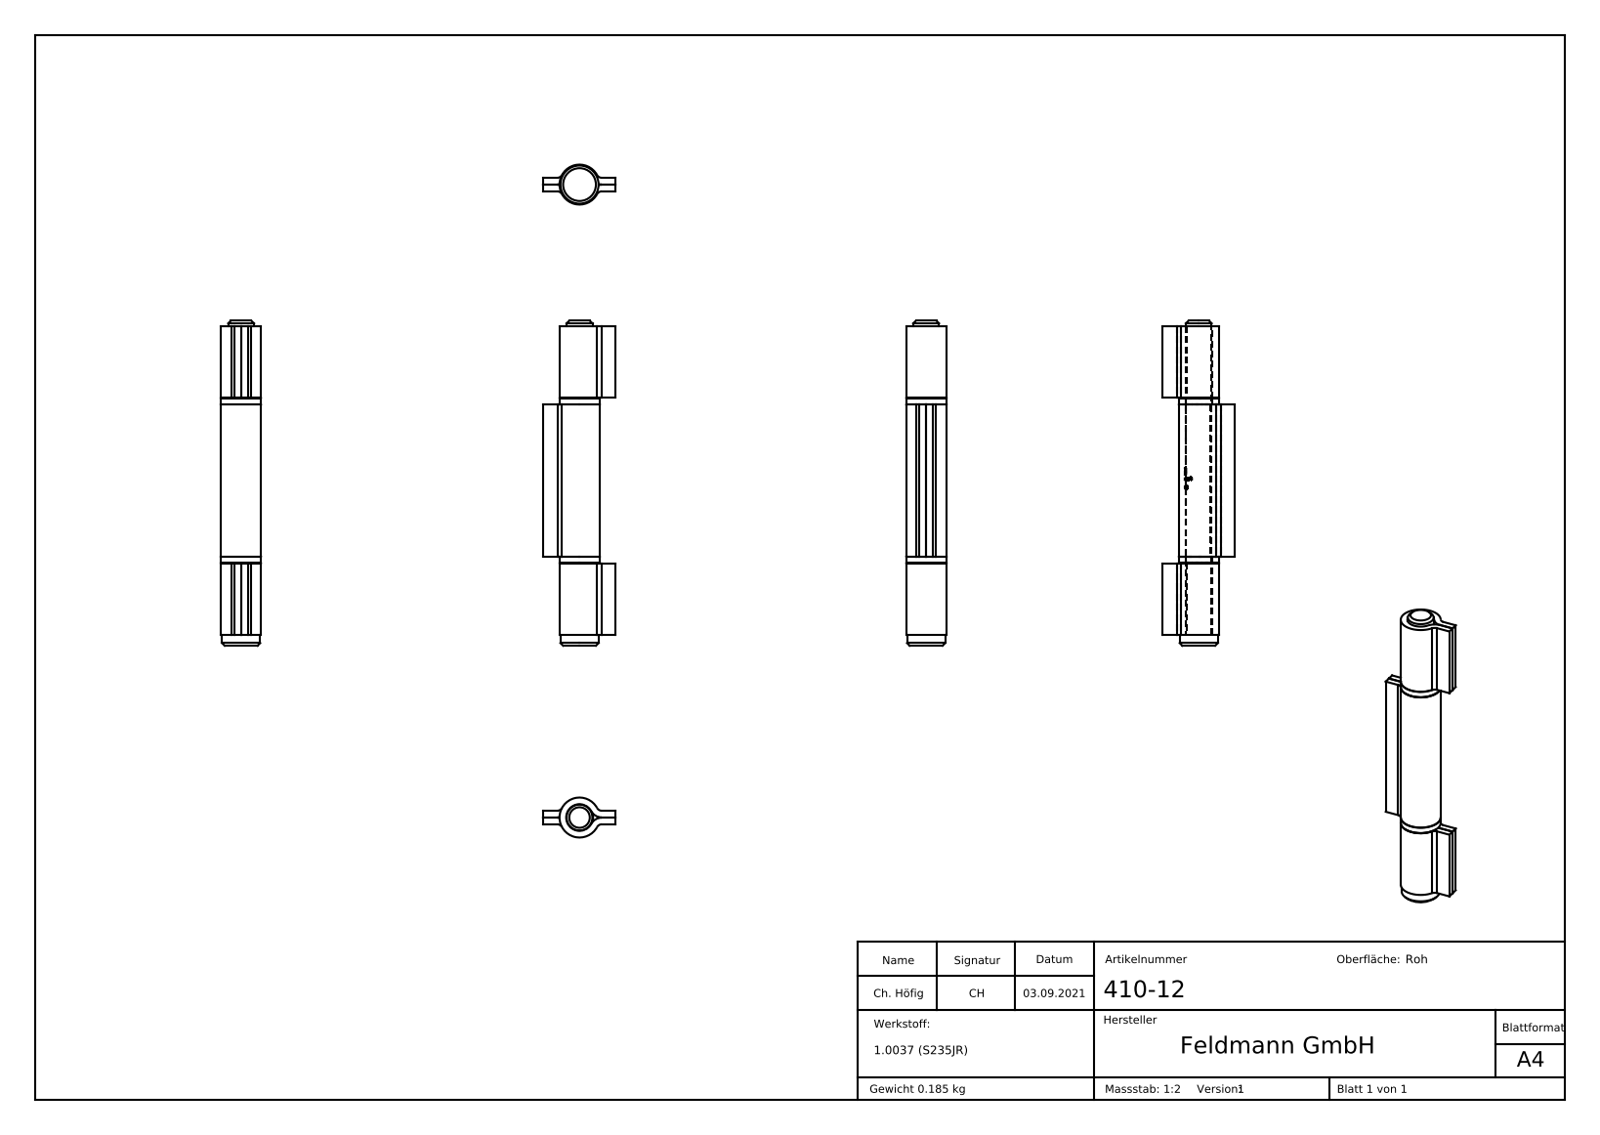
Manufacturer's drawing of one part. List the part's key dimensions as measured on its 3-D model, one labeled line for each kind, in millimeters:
Part name (STEP PRODUCT): 410-xx Teil3; 410-xx Teil4; 410-xx Teil2; 410-xx Teil2_410-12 Teil2 (+5 more)
STEP written by: SolidWorks 2018 (CONFIG_CONTROL_DESIGN)
Units: millimetres
Bodies: 6 solids, 279 faces (142 planar, 44 cylindrical, 93 other)
Overall size (bounding box): 122 × 27 × 15
Volume: 23 778 mm³ · Surface area: 17 312 mm²
Round holes (diameter × count): ⌀10 ×1
Round bosses / shafts (diameter × count): ⌀15 ×1, ⌀14.3 ×1, ⌀9.7 ×1
Partial cylindrical surfaces — rounded edges, fillets, slot ends (radius × count): R2 ×4, R4.5 ×4, R5.1 ×1
Main face-to-face distances: 2.5, 2.6, 27, 5.1, 59.5, 29.5, 86.5, 89, 62, 57
